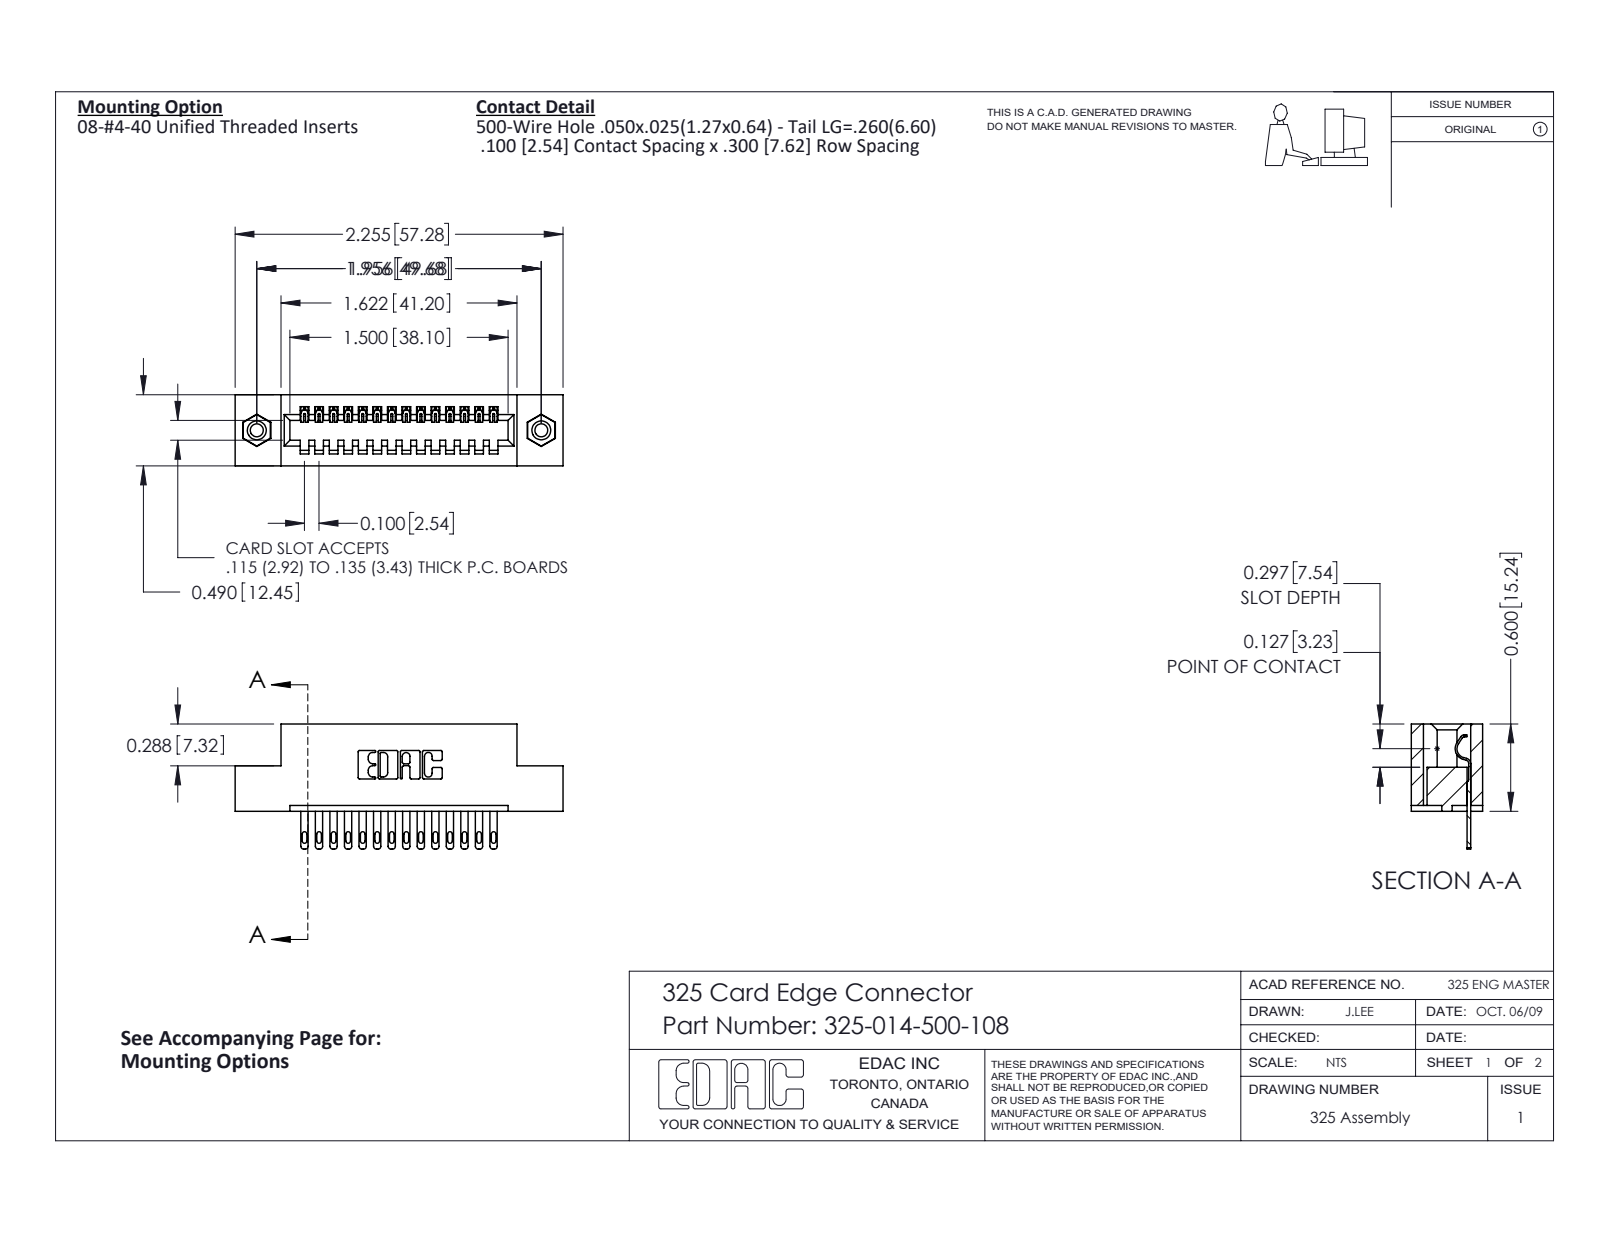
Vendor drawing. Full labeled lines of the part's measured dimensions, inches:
Part name (STEP PRODUCT): 325-292-001_325-293-100; 345-250-001_345-250-003-102; 325 Part_TI; 325-014-500-108
STEP written by: SolidWorks 2016 (CONFIG_CONTROL_DESIGN)
Units: inches
Bodies: 17 solids, 930 faces (606 planar, 308 cylindrical, 16 other)
Overall size (bounding box): 2.255 × 0.86 × 0.49
Volume: 0.43 in³ · Surface area: 11.28 in²
Round holes (diameter × count): ⌀0.089 ×2, ⌀0.125 ×2, ⌀0.16 ×2
Round bosses / shafts (diameter × count): ⌀0.155 ×2
Partial cylindrical surfaces — rounded edges, fillets, slot ends (radius × count): R0.006 ×28, R0.016 ×28, R0.02 ×28, R0.01 ×22, R0.007 ×6, R0.031 ×6, R0.026 ×3, R0.014 ×1
Main face-to-face distances: 0.083, 0.407, 0.3, 0.49, 0.04, 0.107, 0.383, 0.025, 0.1, 0.6
Hole centre spacings: 1.956
